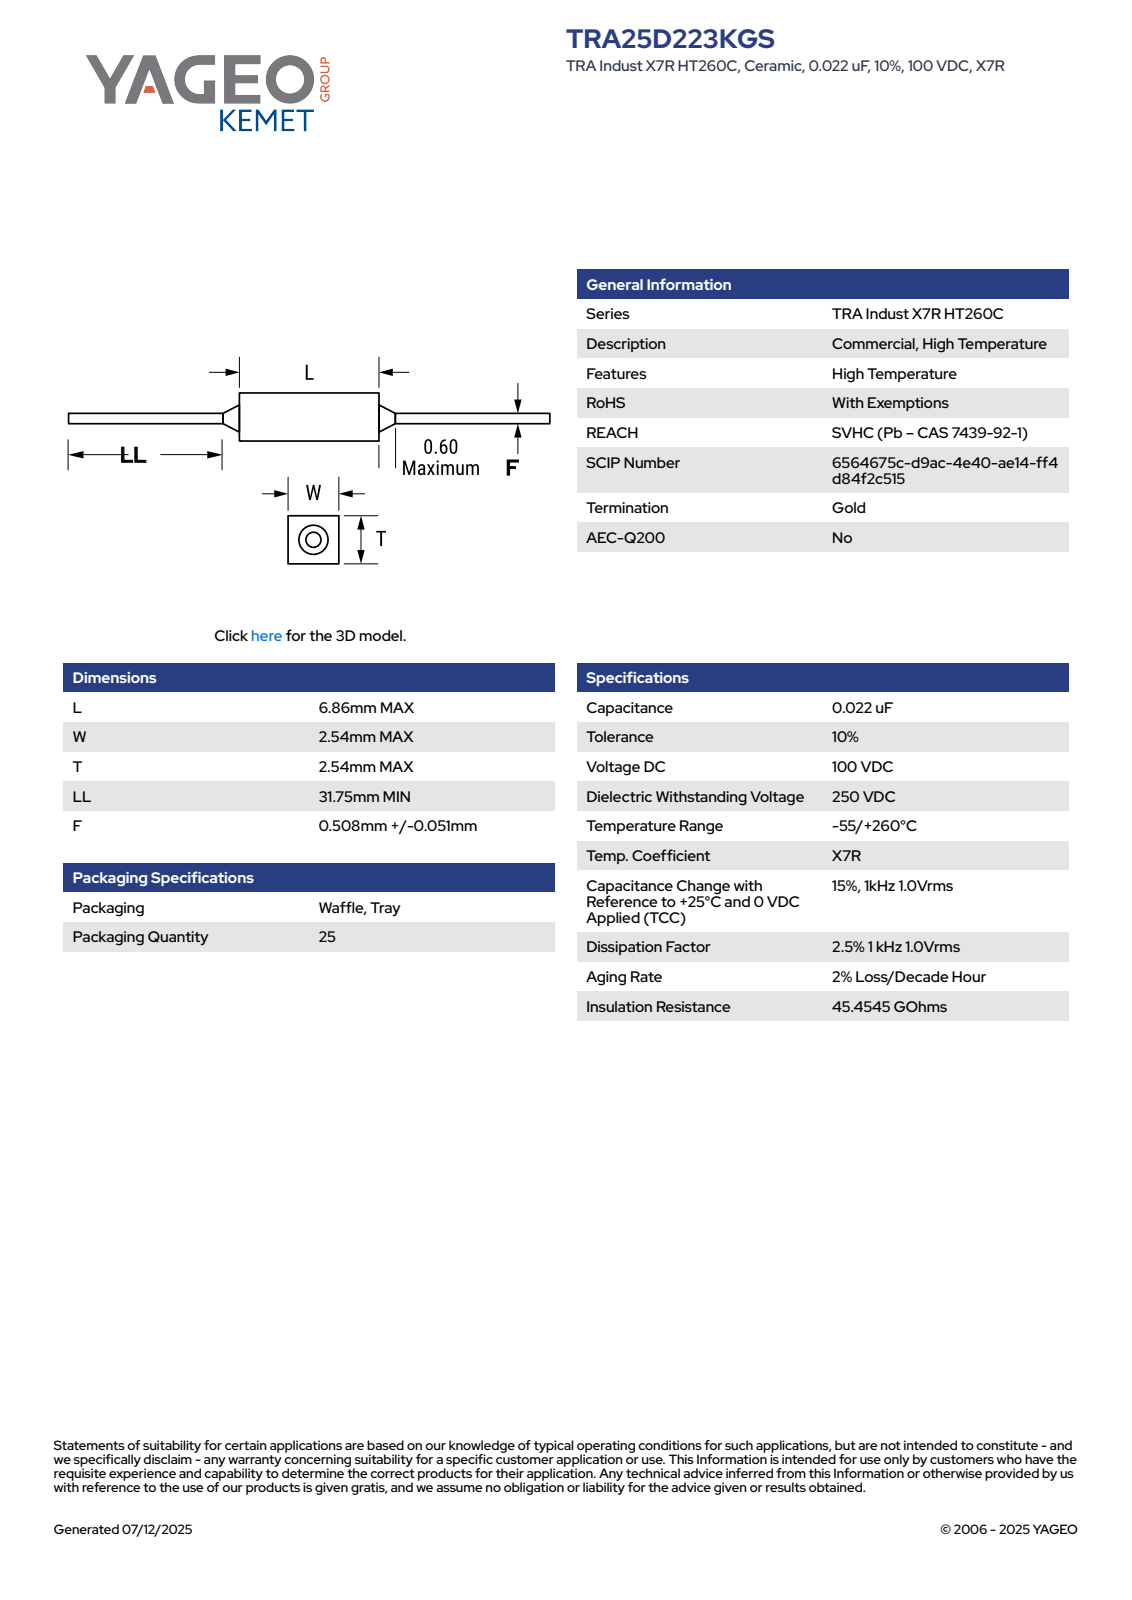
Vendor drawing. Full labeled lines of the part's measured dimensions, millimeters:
Part name (STEP PRODUCT): CCR_C3_25_L6.86T2.54LL31.75F0.559W2.54
STEP written by: SolidWorks 2021 (AUTOMOTIVE_DESIGN)
Units: millimetres
Bodies: 4 solids, 73 faces (65 planar, 4 cylindrical, 4 other)
Overall size (bounding box): 71.56 × 2.54 × 2.54
Volume: 61 mm³ · Surface area: 200 mm²
Round bosses / shafts (diameter × count): ⌀0.56 ×1
Main face-to-face distances: 2.54, 6.86, 32.35, 39.21, 71.56, 1.81, 0.73, 1, 0.81, 1.54
